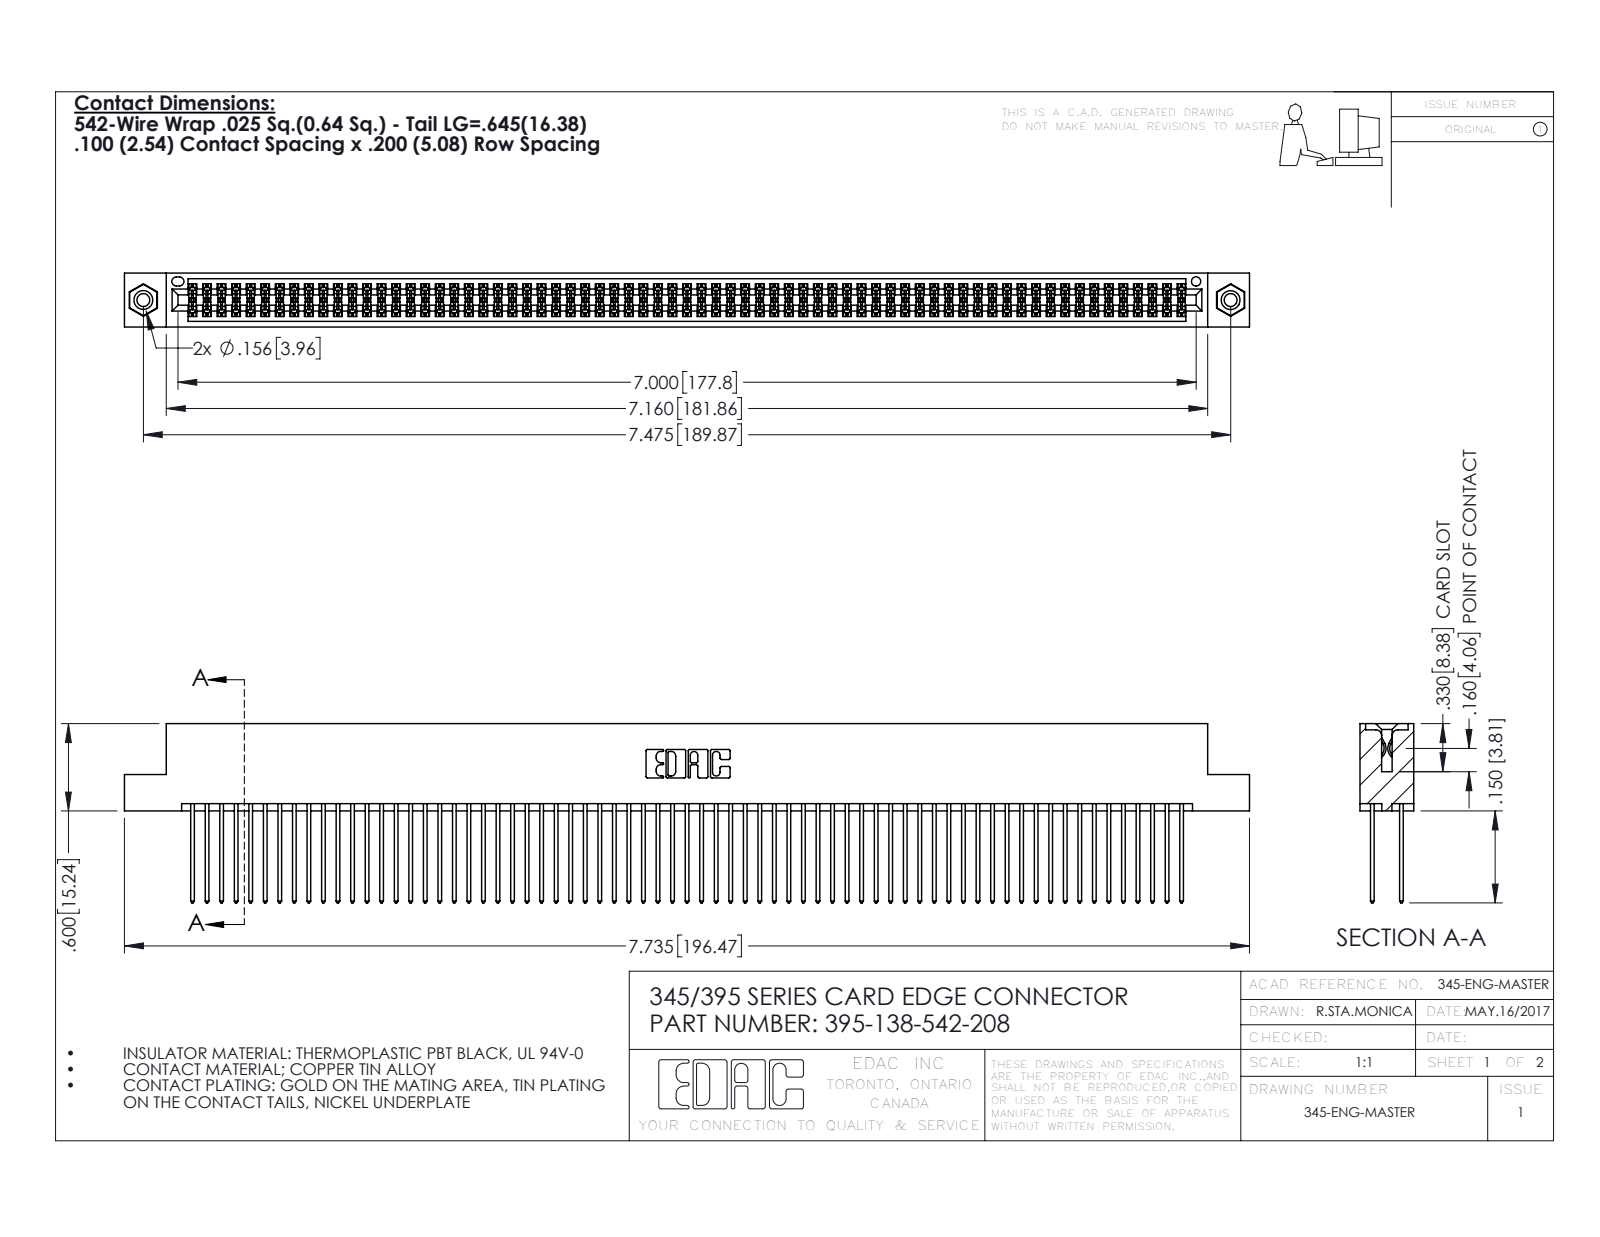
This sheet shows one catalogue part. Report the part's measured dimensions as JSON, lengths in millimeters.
{"part_name": "345 Part_Flush Mounting Lugs - 0.156 Dia-TI; 345-250-001_345-250-003-102; 395-138-542-208; 345-292-001_345-293-142", "step_written_by": "SolidWorks 2016 (CONFIG_CONTROL_DESIGN)", "units": "millimeters", "bodies": {"solids": 141, "faces": 7086, "planar": 4666, "cylindrical": 2404, "other": 16}, "overall_size": [196.5, 31.3, 9.4], "volume_mm3": 19980, "surface_area_mm2": 33060, "round_holes": [[2.3, 2], [3.2, 2], [4, 2], [1.6, 1]], "round_bosses_or_shafts": [[3.9, 2]], "partial_cylinders_radius": [[0.2, 207], [0.3, 138], [0.3, 22], [0.2, 6], [0.8, 6], [0.7, 3], [0.4, 2], [0.5, 2]], "face_to_face_distances": [1.8, 7.6, 5.1, 2.5, 6.9, 0.6, 5.7, 9.4, 4.4, 3.8], "hole_center_spacings": [6.9, 183.9, 189.9]}
